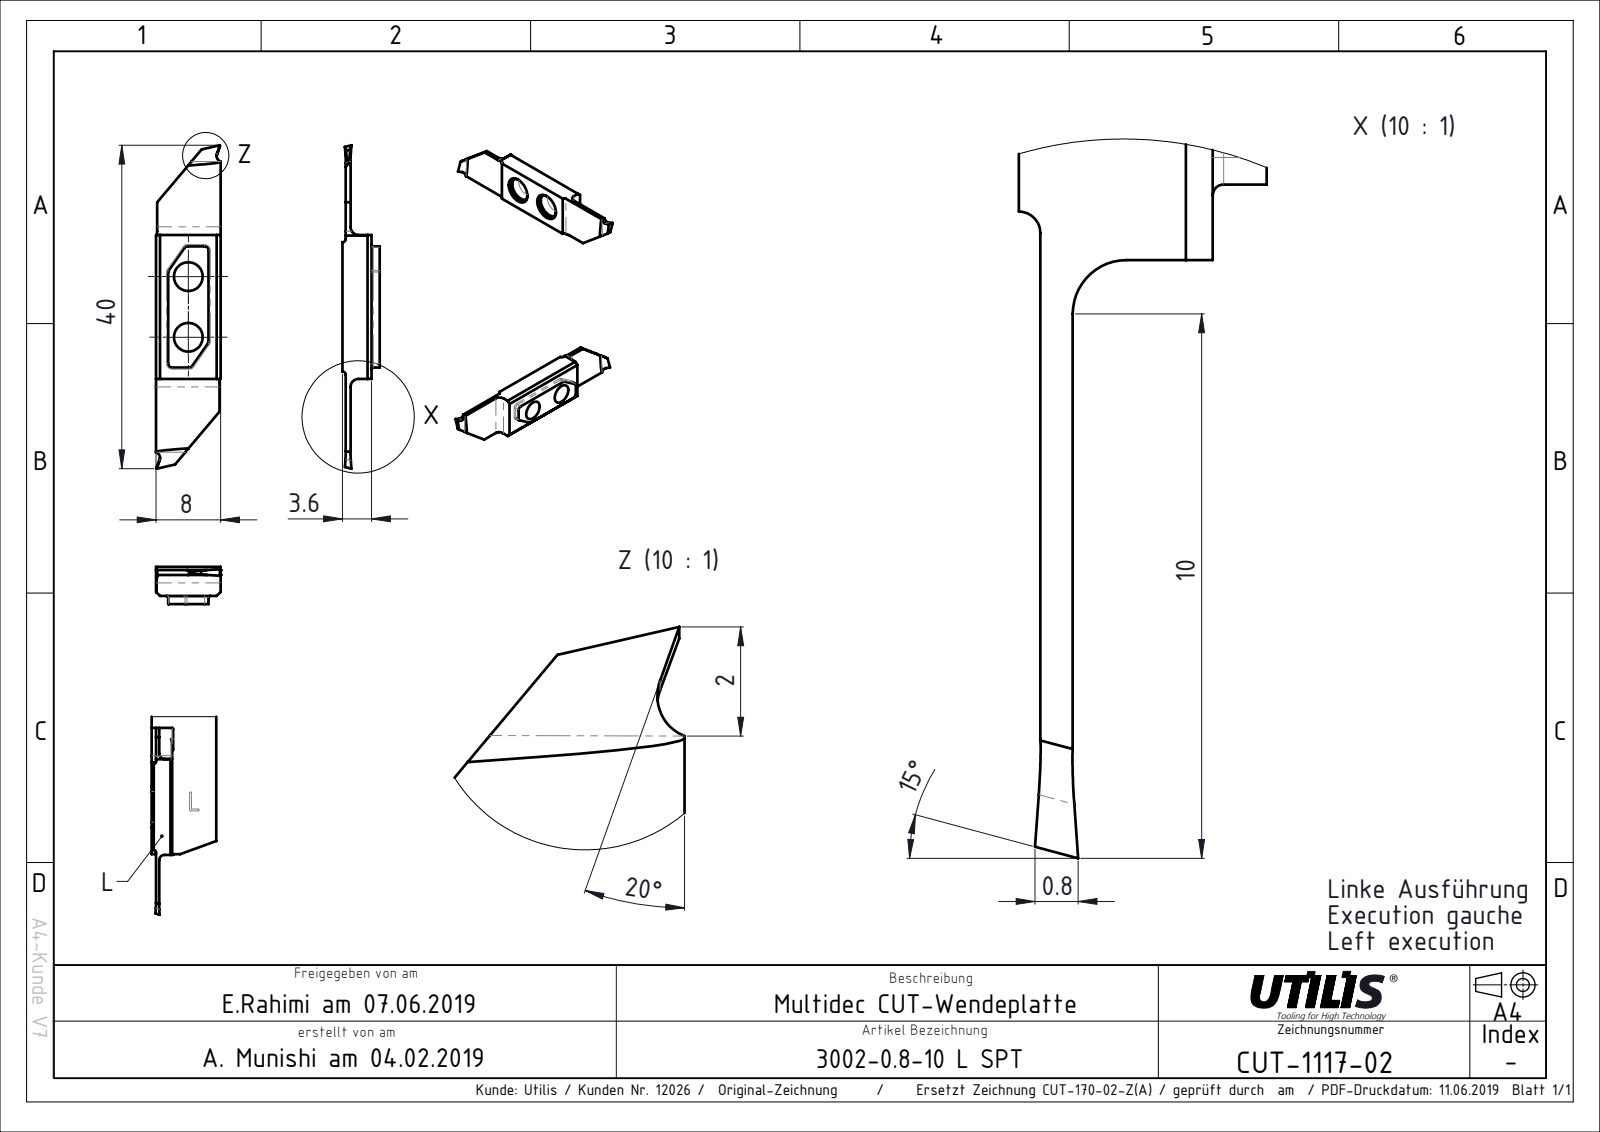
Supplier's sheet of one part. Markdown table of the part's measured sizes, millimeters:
| quantity | value |
| --- | --- |
| part name | CUT-1117; ASME Y14.5 |
| STEP written by | FormatWorks Professional (AP242_MANAGED_MODEL_BASED_3D_ENGINEERING_MIM_LF) |
| units | millimeters |
| bodies | 1 solid, 34 faces (24 planar, 10 cylindrical, 0 other) |
| overall size | 40 × 8 × 3.6 |
| volume | 514 mm³ |
| surface area | 777 mm² |
| round holes (diameter × count) | 3.55 × 2 |
| partial cylindrical surfaces (radius × count) | 1 × 4, 0.4 × 2 |
| main face-to-face distances | 0.41, 0.99, 0.58, 3.6, 3.19, 2.61, 8, 17.8, 22.54, 7.85 |
| hole center spacings | 7.5 |
